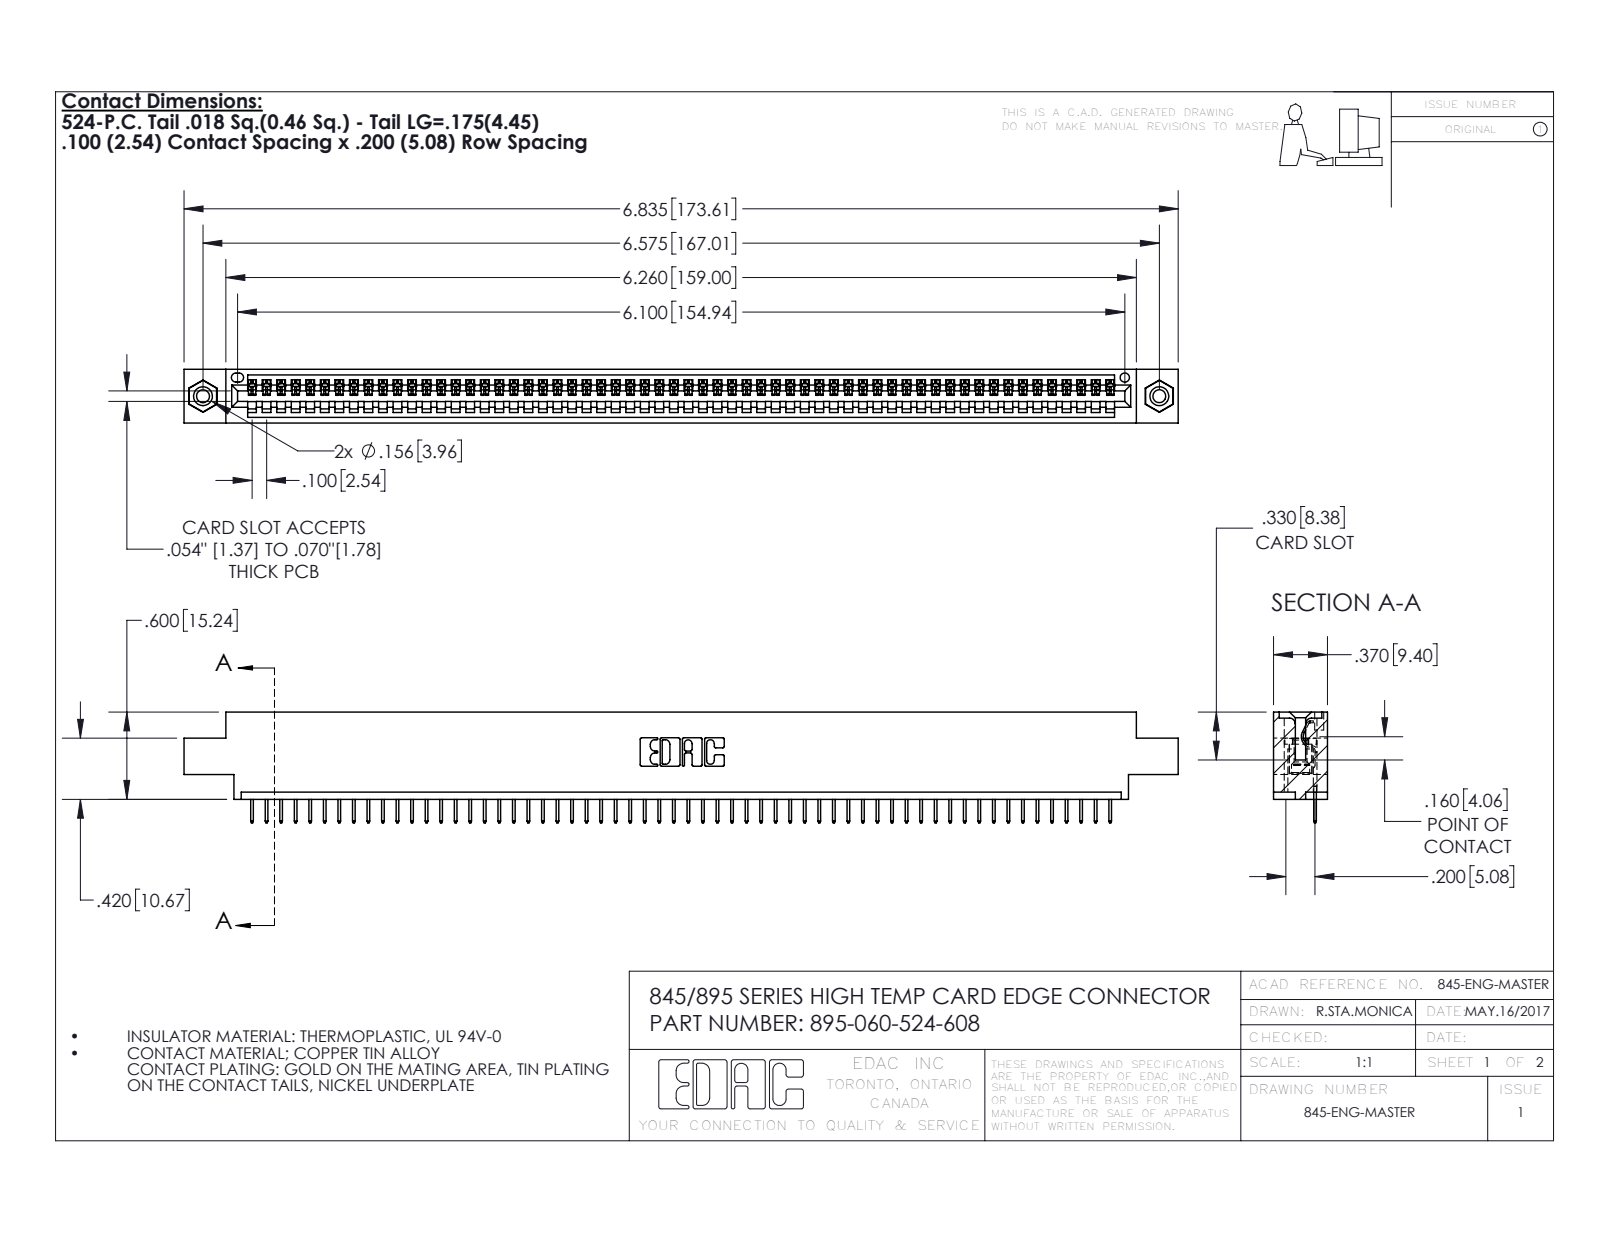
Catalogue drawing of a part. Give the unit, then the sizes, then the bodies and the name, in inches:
Units: inches
Overall size (bounding box): 6.835 × 0.762 × 0.37
Round holes (diameter × count): ⌀0.089 ×2, ⌀0.125 ×2, ⌀0.156 ×2, ⌀0.064 ×1
Round bosses / shafts (diameter × count): ⌀0.155 ×2
Partial cylindrical surfaces — rounded edges, fillets, slot ends (radius × count): R0.006 ×120, R0.01 ×22, R0.007 ×6, R0.031 ×6, R0.026 ×3, R0.031 ×2, R0.04 ×2, R0.014 ×1
Main face-to-face distances: 0.072, 0.298, 0.37, 0.2, 0.098, 0.272, 0.025, 0.225, 0.072, 0.175
Hole centre spacings: 0.27, 6.339, 6.575
Volume: 0.993 in³ · Surface area: 32.96 in²
Bodies: 63 solids, 3910 faces (2876 planar, 1018 cylindrical, 16 other)
Part name (STEP PRODUCT): 395-060-524-608; 345-292-001_345-293-124; 345 Part_0.170 Offset - 0.156 Dia-TI; 345-250-001_345-250-003-102
STEP written by: SolidWorks 2016 (CONFIG_CONTROL_DESIGN)
